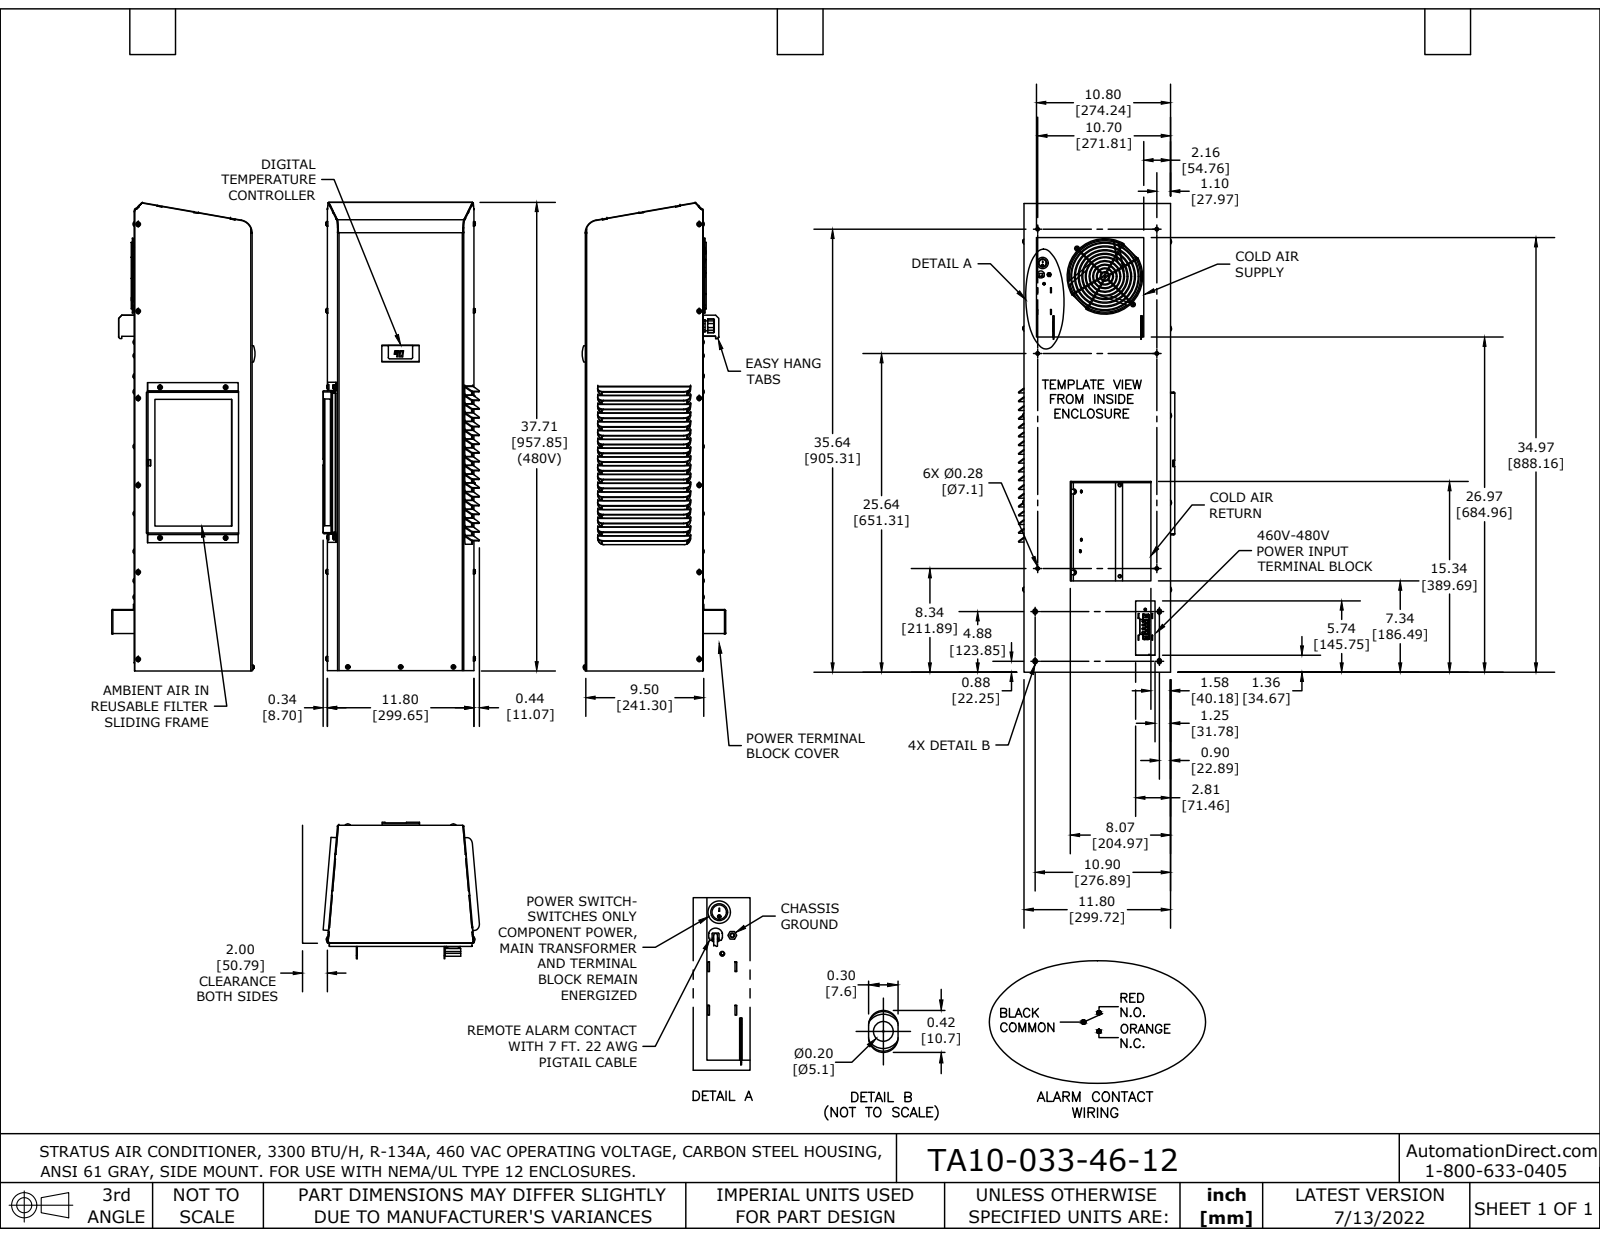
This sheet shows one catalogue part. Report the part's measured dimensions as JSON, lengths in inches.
{"part_name": "TA10-033-46-12", "step_written_by": "SolidWorks 2021 (AUTOMOTIVE_DESIGN)", "units": "inches", "bodies": {"solids": 1, "faces": 1956, "planar": 1208, "cylindrical": 567, "other": 181}, "overall_size": [32.024, 12.576, 11.554], "volume_in3": 144.5, "surface_area_in2": 3631, "round_holes": [[0.194, 17], [0.219, 15], [0.159, 11], [0.204, 5], [0.099, 3], [0.4, 2], [0.136, 1], [6, 1]], "round_bosses_or_shafts": [[0.19, 7], [0.353, 2], [0.248, 2], [6.07, 1], [0.906, 1], [0.395, 1], [0.386, 1], [0.087, 1]], "partial_cylinders_radius": [[0.015, 45], [0.01, 42], [0.5, 36], [0.506, 36], [0.1, 28], [0.058, 21], [0.116, 21], [0.032, 15]], "face_to_face_distances": [0.058, 9.377, 9.435, 9.431, 0.054, 9.489, 0.037, 0.058, 0.373, 0.254], "hole_center_spacings": [7, 14, 5.4, 7.068, 8.894, 21, 0.524, 2.861]}
